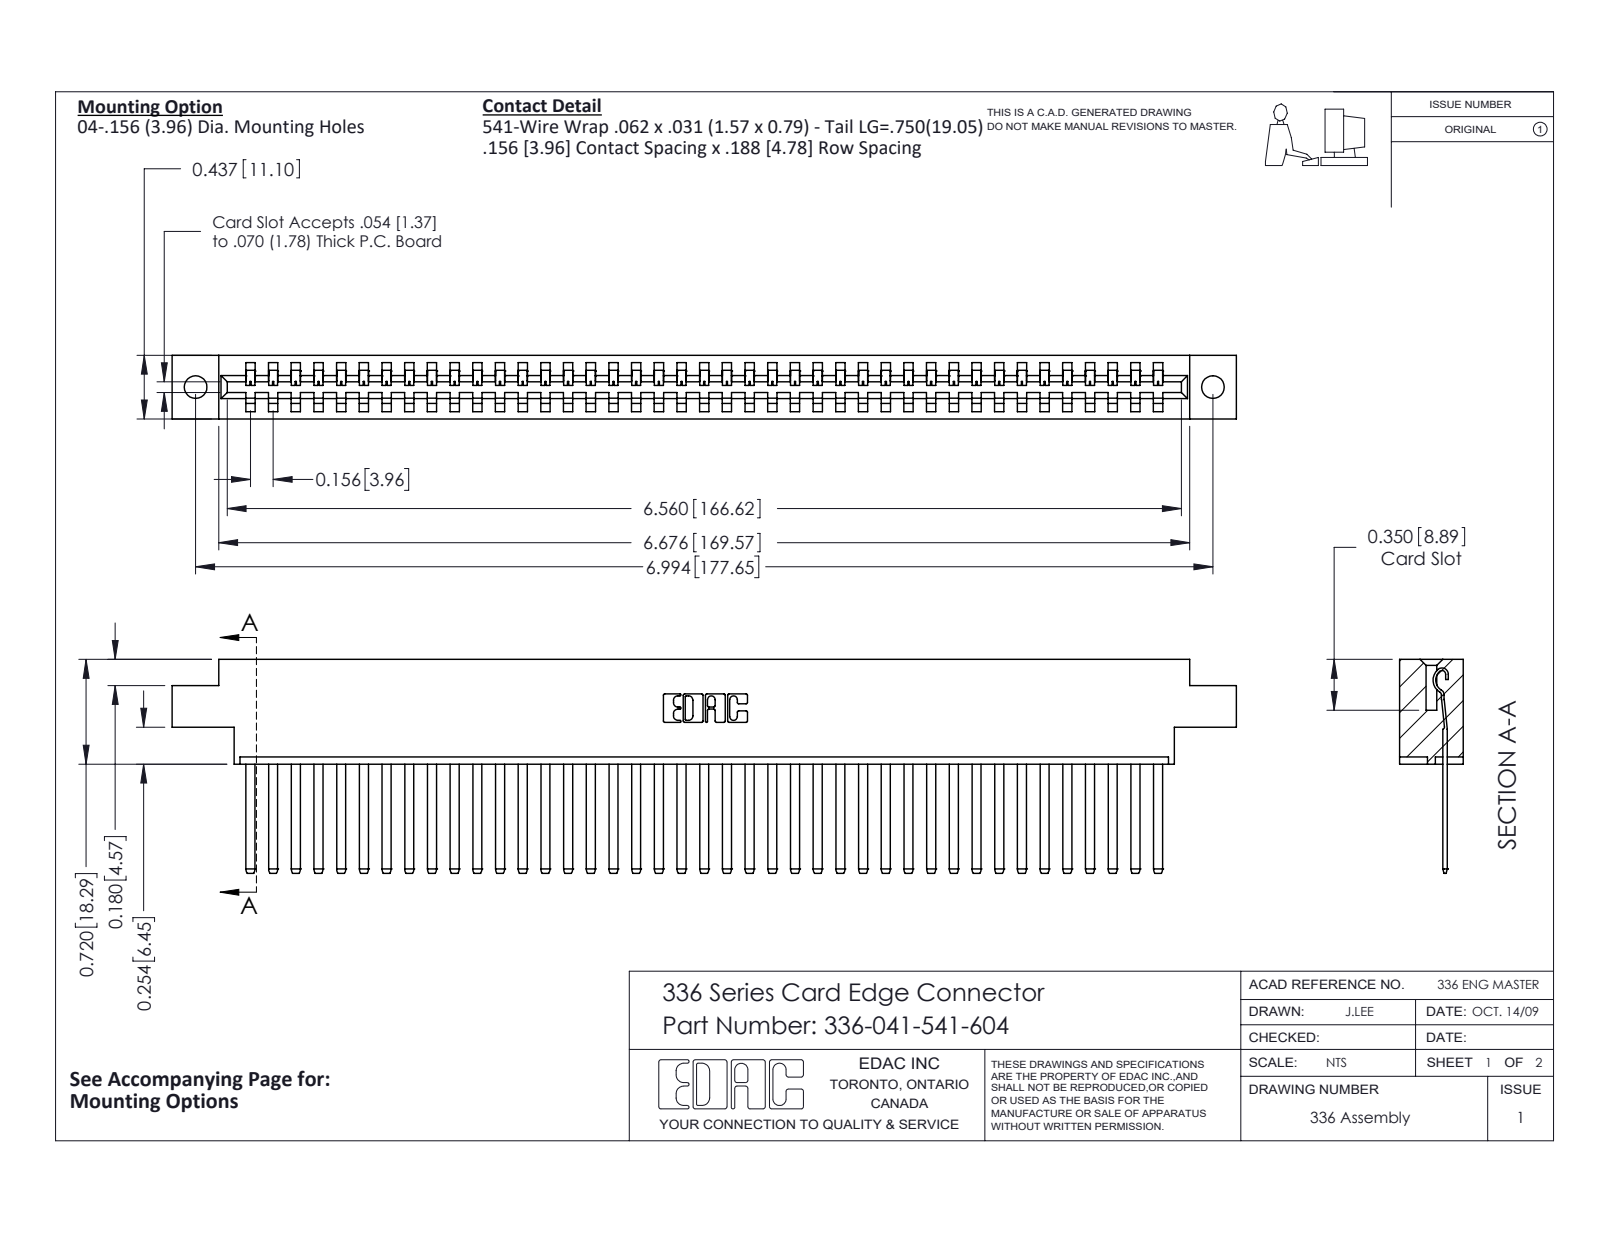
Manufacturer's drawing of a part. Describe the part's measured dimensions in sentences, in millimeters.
The part is named "336 Part_Offset - .156 Dia - TH; 336-041-541-604; 336-290-001_336-290-541". Its 3-D file was written by "SolidWorks 2020 (CONFIG_CONTROL_DESIGN)". It is 42 solids with 2168 faces: 1468 planar, 700 cylindrical and 0 other. Overall it measures 185.9 by 37.3 by 11.1 millimeters. Its volume is 26 960 cubic millimeters and its surface area 29 210 square millimeters. Round holes: 2 of diameter 4. Partial cylindrical surfaces (rounded edges, fillets, slot ends): 82 of radius 0.1, 82 of radius 1.4, 22 of radius 0.3, 6 of radius 0.2, 6 of radius 0.8, 3 of radius 0.7, 2 of radius 0.6, 2 of radius 1. The main face-to-face distances are 11.1, 4.6, 8.3, 3.6, 7.5, 2.8, 0.8, 6.5, 1.3, 9.8. The hole center spacings are 177.6.
